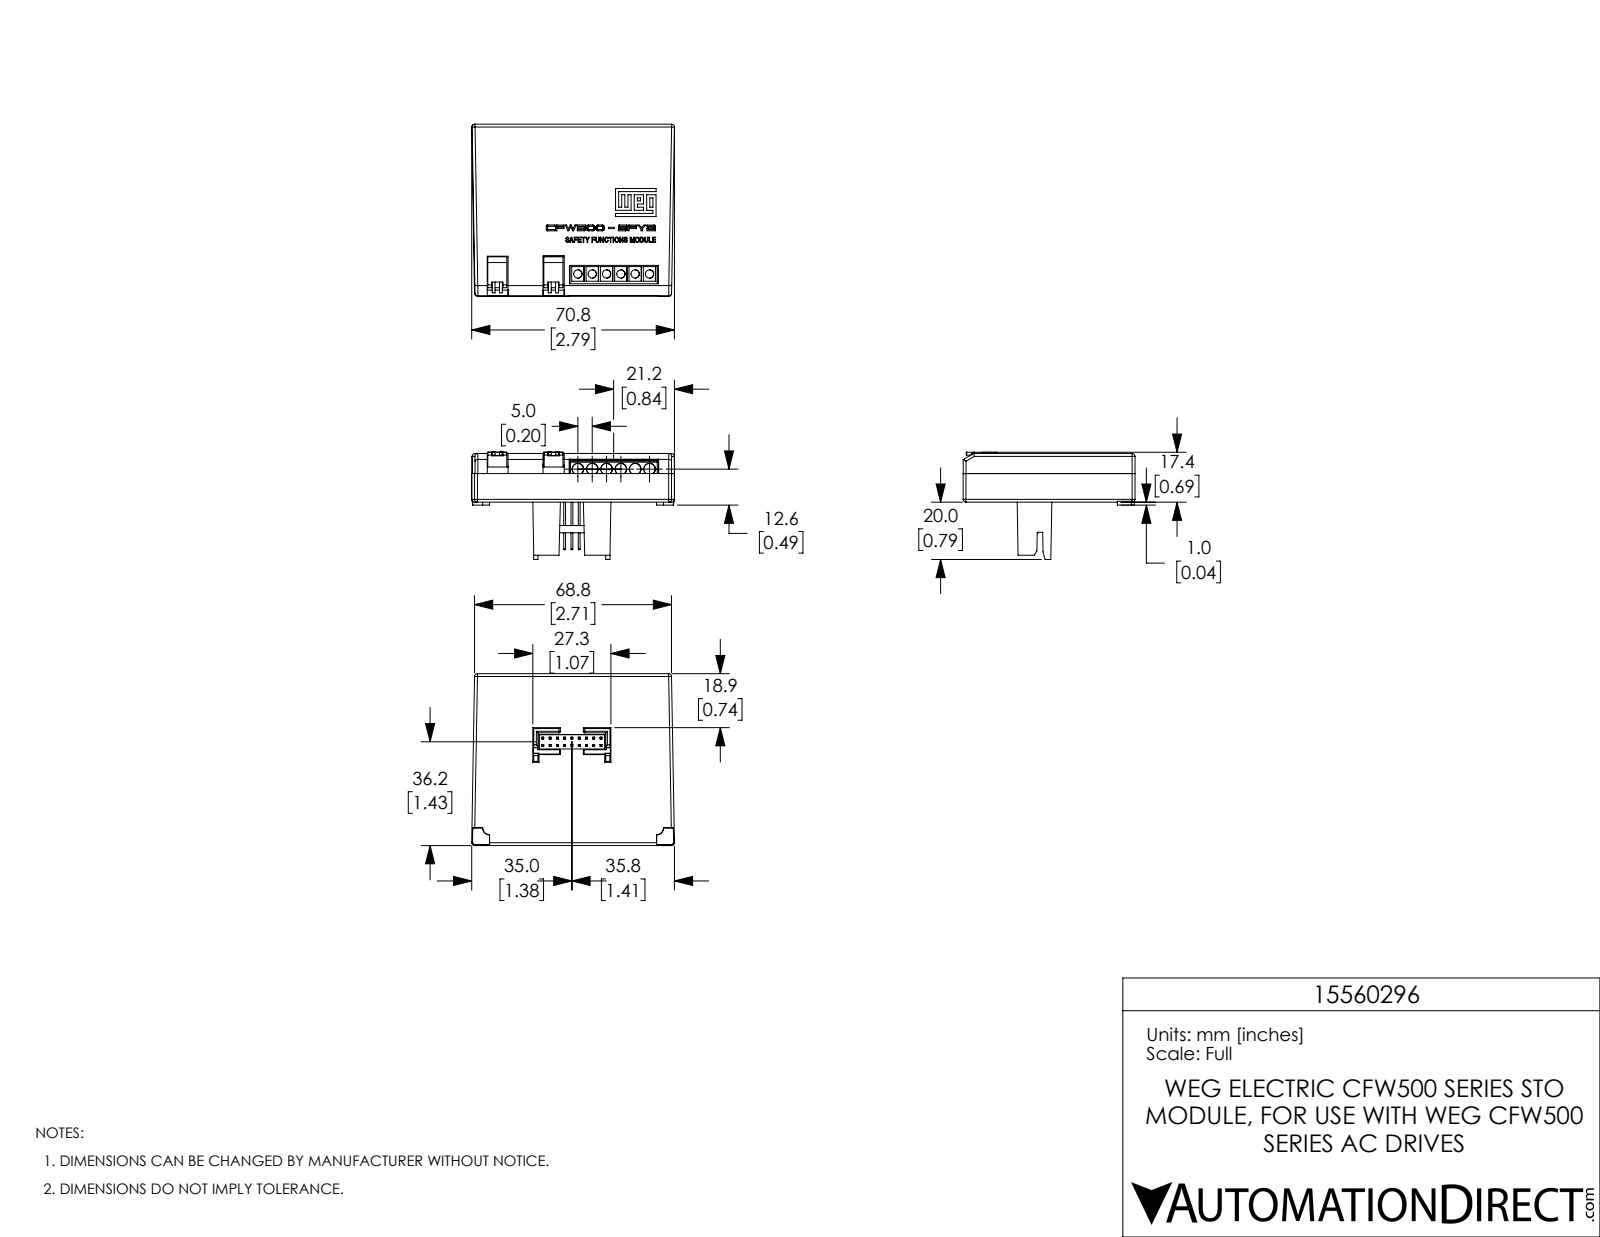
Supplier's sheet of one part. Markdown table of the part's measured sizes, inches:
| quantity | value |
| --- | --- |
| part name | 15560296 |
| STEP written by | SolidWorks 2017 (AUTOMOTIVE_DESIGN) |
| units | inches |
| bodies | 6 solids, 1453 faces (1239 planar, 109 cylindrical, 105 other) |
| overall size | 2.788 × 2.363 × 1.474 |
| volume | 4.435 in³ |
| surface area | 42.13 in² |
| round holes (diameter × count) | 0.114 × 6, 0.157 × 6 |
| round bosses / shafts (diameter × count) | 0.051 × 6 |
| partial cylindrical surfaces (radius × count) | 0.039 × 19, 0.012 × 12, 0.007 × 2, 0.032 × 2 |
| main face-to-face distances | 0.394, 0.669, 0.276, 0.059, 2.363, 0.1, 0.425, 0.434, 0.115, 0.433 |
| hole center spacings | 0.197, 0.394, 0.591, 0.787, 0.984 |
